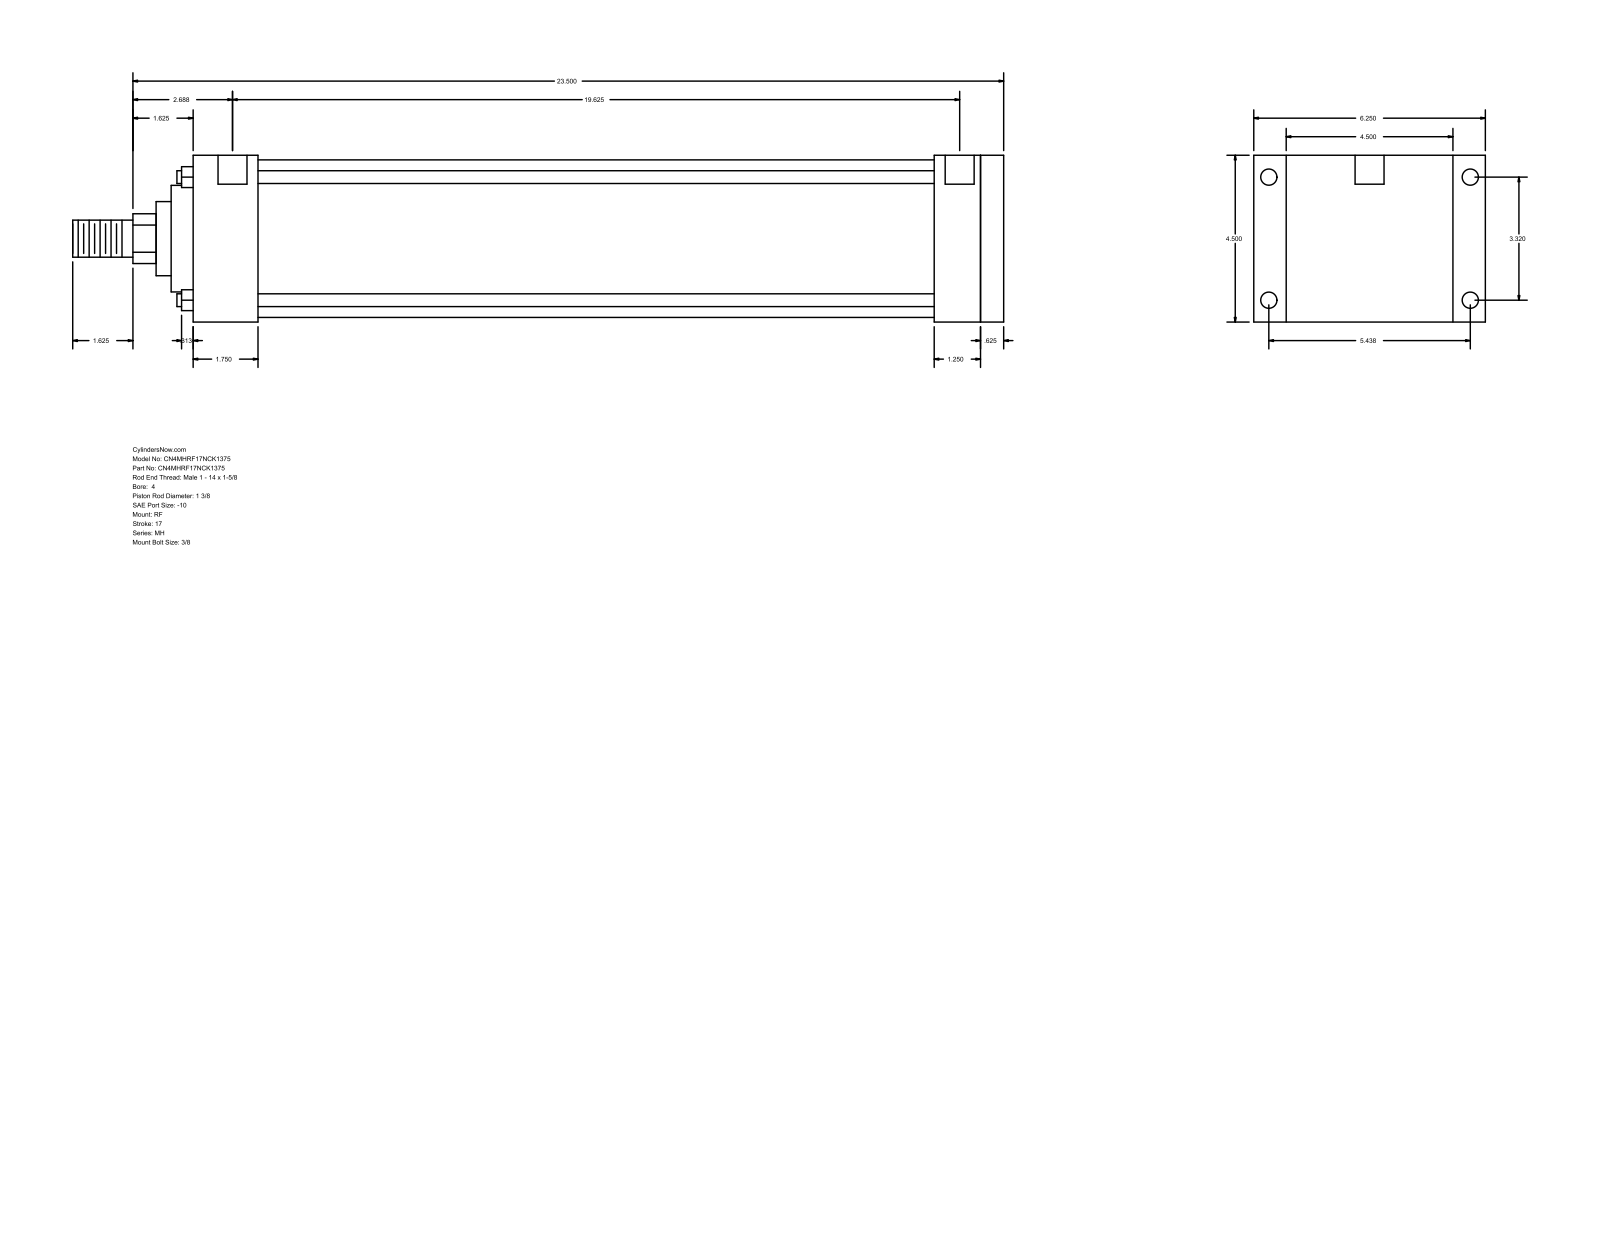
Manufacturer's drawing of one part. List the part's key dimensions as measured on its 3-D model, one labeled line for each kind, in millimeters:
Part name (STEP PRODUCT): MH_RF__0400_1.375
STEP written by: GSSL Pune (CONFIG_CONTROL_DESIGN)
Units: millimetres
Bodies: 0 solids, 94 faces (65 planar, 29 cylindrical, 0 other)
Overall size (bounding box): 638.17 × 158.75 × 114.3
Round holes (diameter × count): ⌀8.73 ×4, ⌀11.13 ×4, ⌀19.84 ×2
Round bosses / shafts (diameter × count): ⌀8.76 ×4, ⌀107.95 ×1, ⌀73.03 ×1, ⌀50.8 ×1, ⌀34.92 ×1, ⌀25.4 ×1
Partial cylindrical surfaces — rounded edges, fillets, slot ends (radius × count): R17.06 ×1
Main face-to-face distances: 114.3, 555.63, 15.88, 539.75, 44.45, 495.3, 511.18, 508, 463.55, 31.75
Hole centre spacings: 1.59, 84.32, 138.12, 161.82, 500.07, 501.66, 498.48
